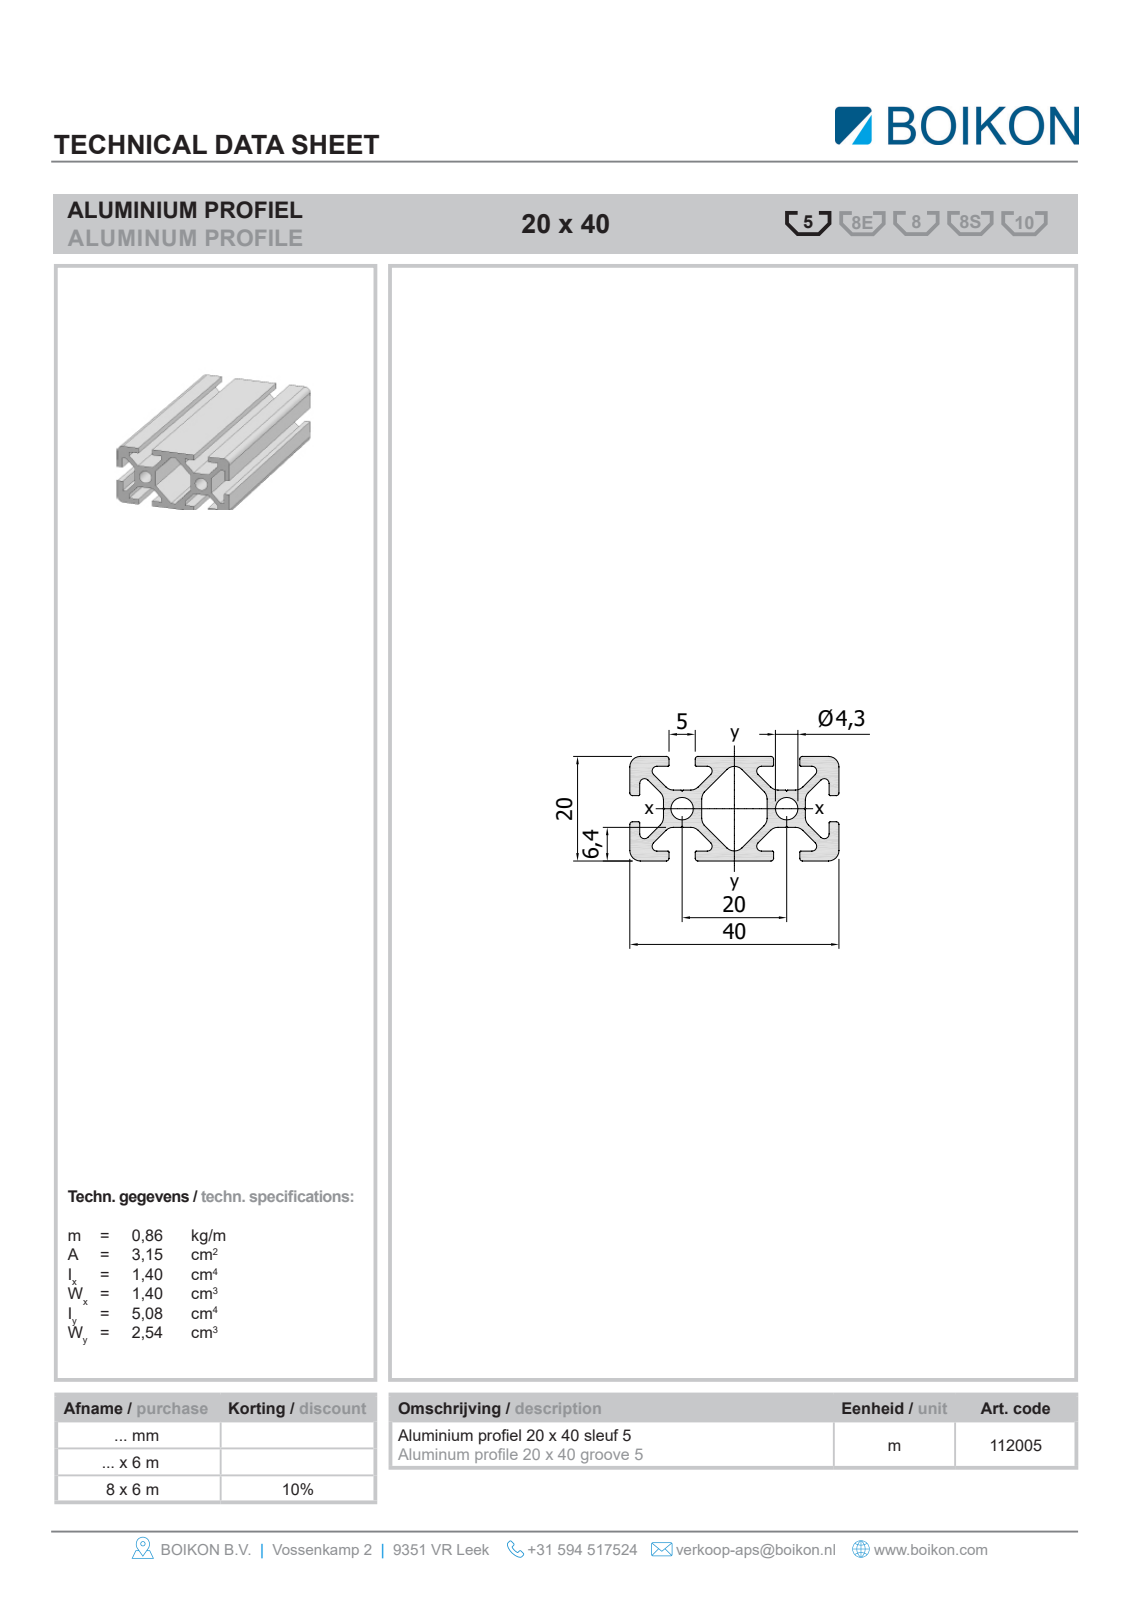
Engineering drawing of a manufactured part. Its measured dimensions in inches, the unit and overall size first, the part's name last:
Units: inches
Overall size (bounding box): 39.37 × 1.575 × 0.787
Round holes (diameter × count): ⌀0.169 ×2
Partial cylindrical surfaces — rounded edges, fillets, slot ends (radius × count): R0.079 ×4
Main face-to-face distances: 0.787, 0.071, 0.059, 0.557, 0.248, 0.177, 0.539, 0.469, 0.717, 0.498
Hole centre spacings: 0.787
Volume: 19.25 in³ · Surface area: 498.7 in²
Bodies: 1 solid, 80 faces (74 planar, 6 cylindrical, 0 other)
Part name (STEP PRODUCT): Root; 11200520x40BOIKON0
STEP written by: HiCAD 2013 1802.4 Build 509 (AUTOMOTIVE_DESIGN)
